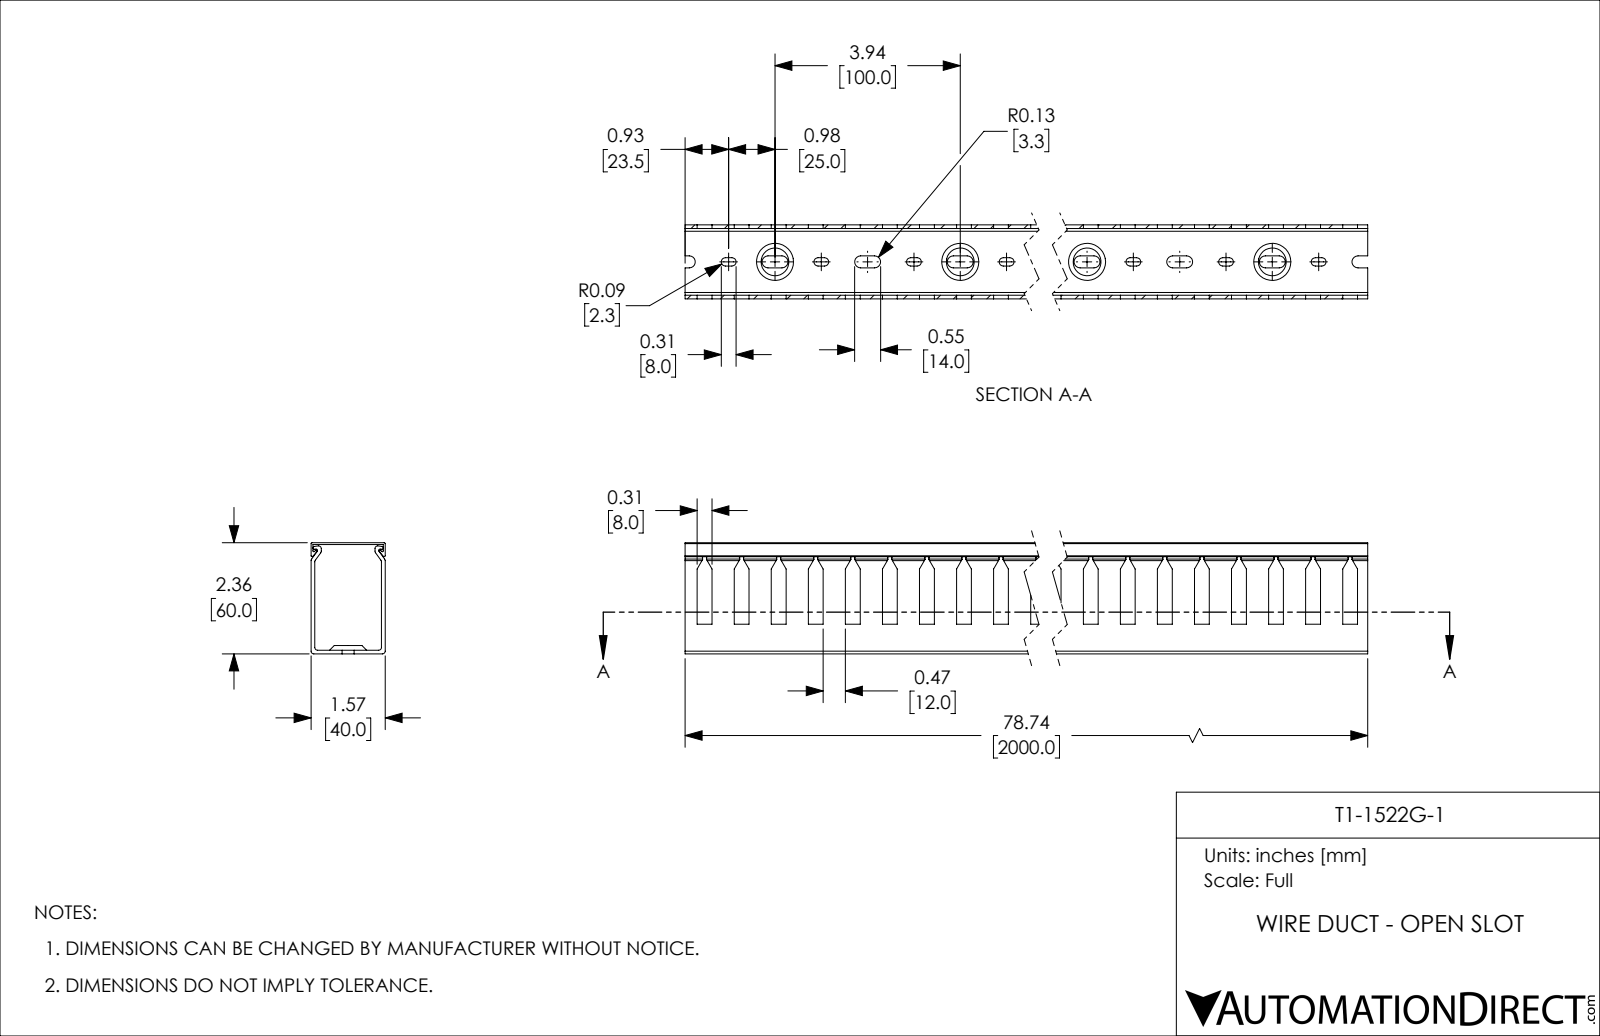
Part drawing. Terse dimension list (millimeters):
name: T1-1522G-1
written by: SolidWorks 2021 (CONFIG_CONTROL_DESIGN)
unit: mm
bodies: 2 solids, 1005 faces (534 planar, 431 cylindrical, 40 other)
size: 2000 × 60 × 40
volume: 736 952 mm³; area: 853 222 mm²
rounds: 80× R2.25, 80× R3.25, 12× R1.5, 8× R0.5, 6× R0.75
face distances: 2, 38, 40, 1, 36, 60, 59, 57, 58, 39
